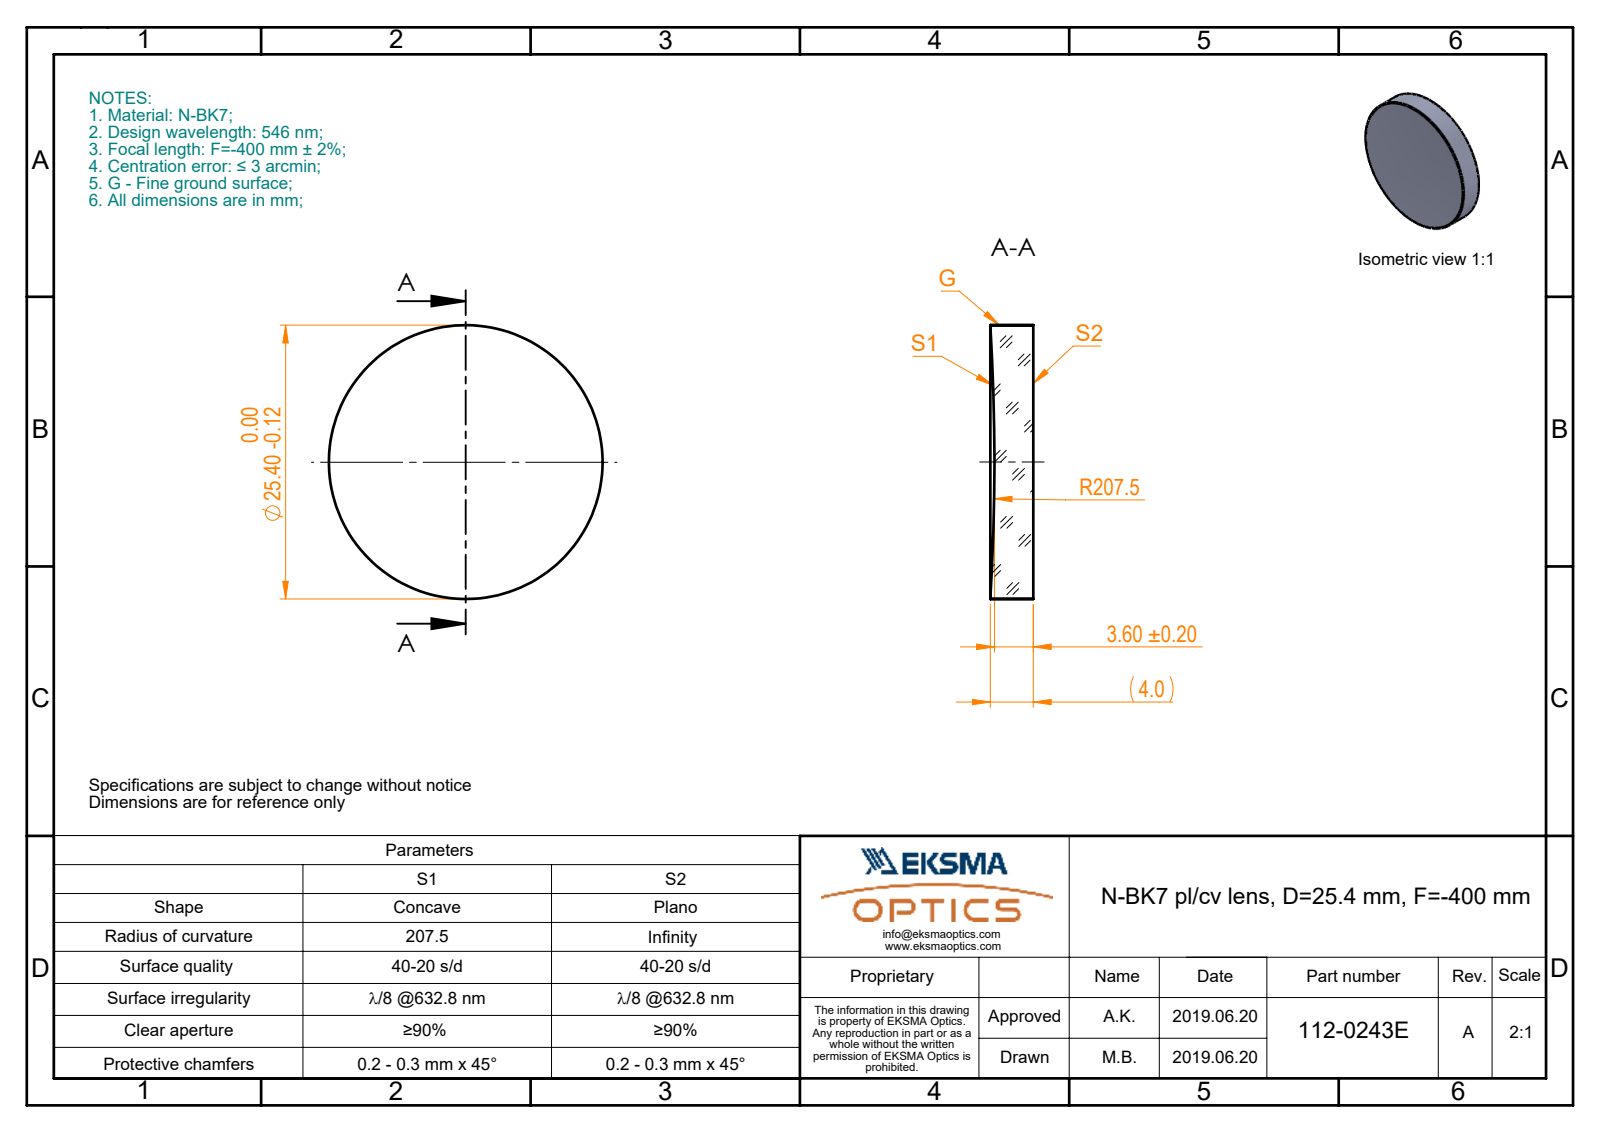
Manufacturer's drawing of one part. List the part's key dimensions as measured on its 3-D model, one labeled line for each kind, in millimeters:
Part name (STEP PRODUCT): 112-0243E BK7 pl-cv 25.4 F-400
STEP written by: SolidWorks 2017 (CONFIG_CONTROL_DESIGN)
Units: millimetres
Bodies: 1 solid, 5 faces (1 planar, 2 cylindrical, 2 other)
Overall size (bounding box): 25.4 × 25.4 × 3.99
Volume: 1 923 mm³ · Surface area: 1 332 mm²
Round bosses / shafts (diameter × count): ⌀25.4 ×1
